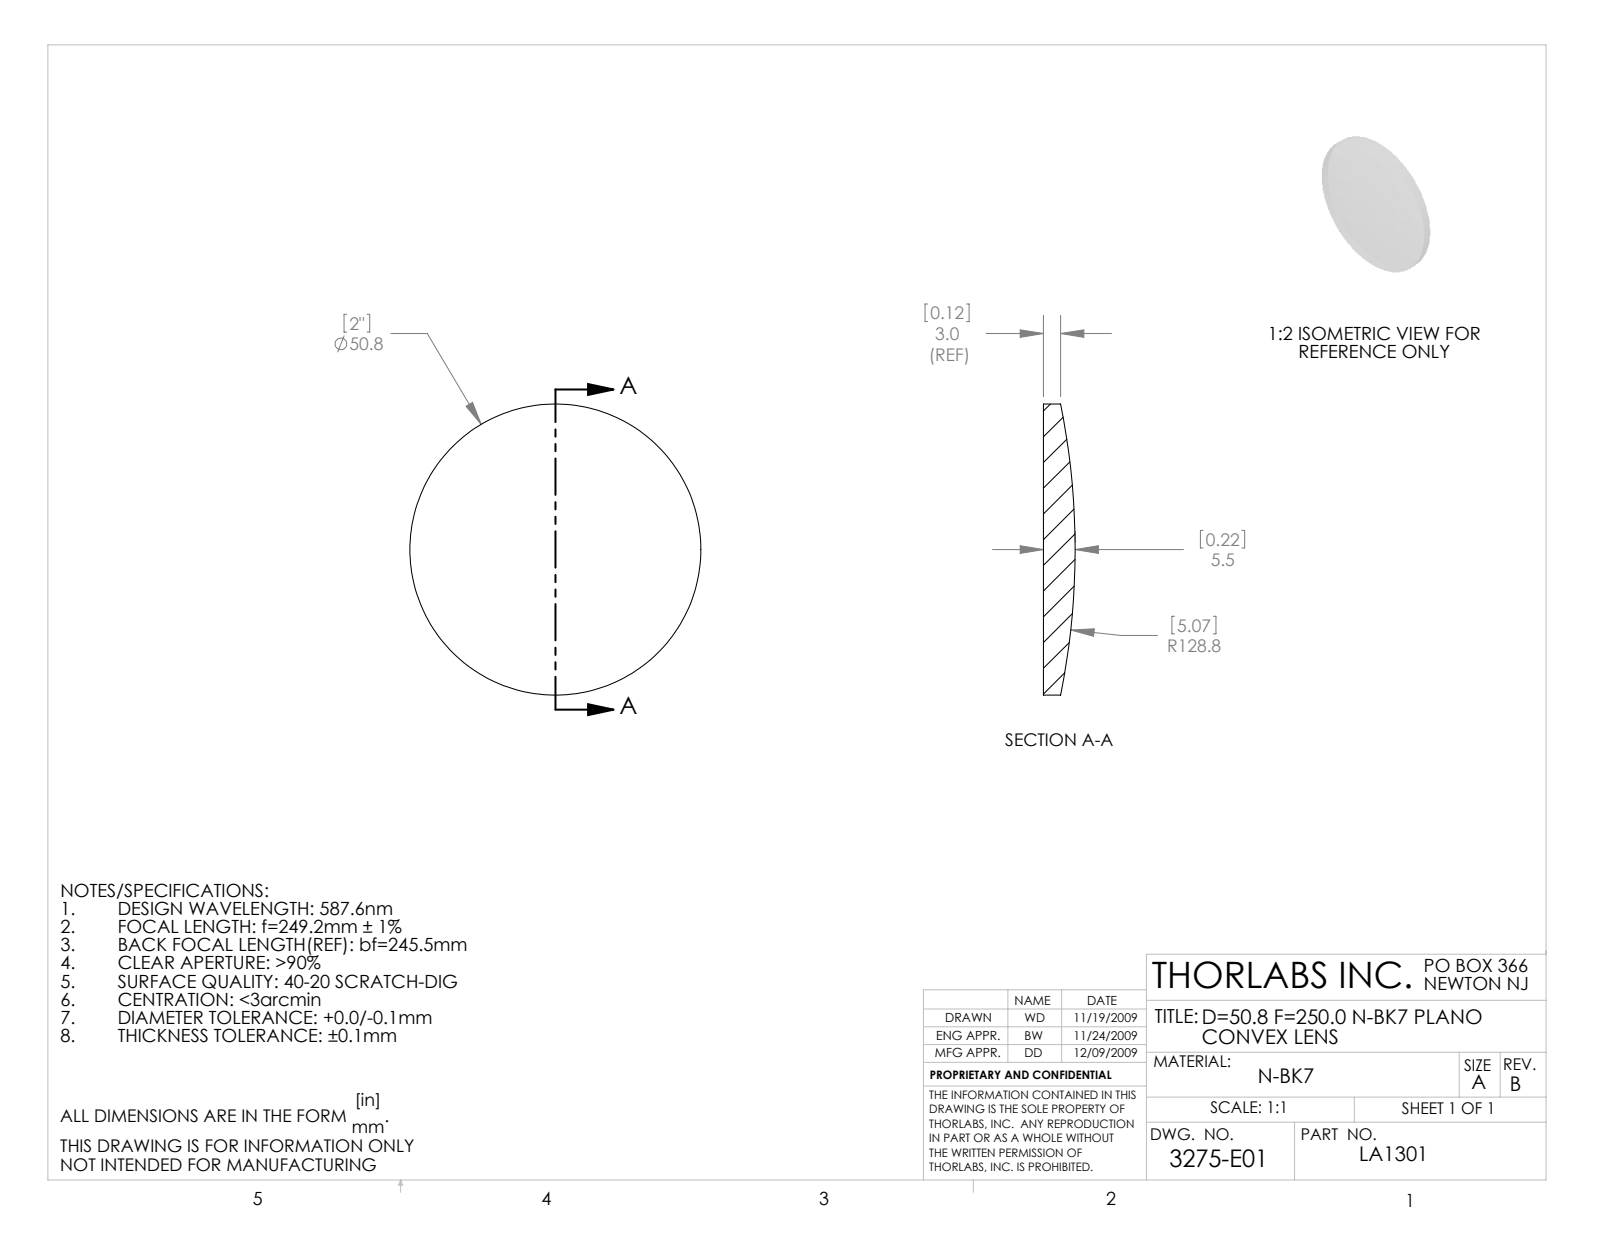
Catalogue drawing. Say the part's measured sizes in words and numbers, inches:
The part is named "3275-E0W". Its 3-D file was written by "SolidWorks 2009 (AUTOMOTIVE_DESIGN)". It is 1 solid with 5 faces: 1 planar, 2 cylindrical and 2 other. Overall it measures 2 by 2 by 0.217 inches. Its volume is 0.527 cubic inches and its surface area 7.054 square inches. Round bosses or shafts: 1 of diameter 2.
